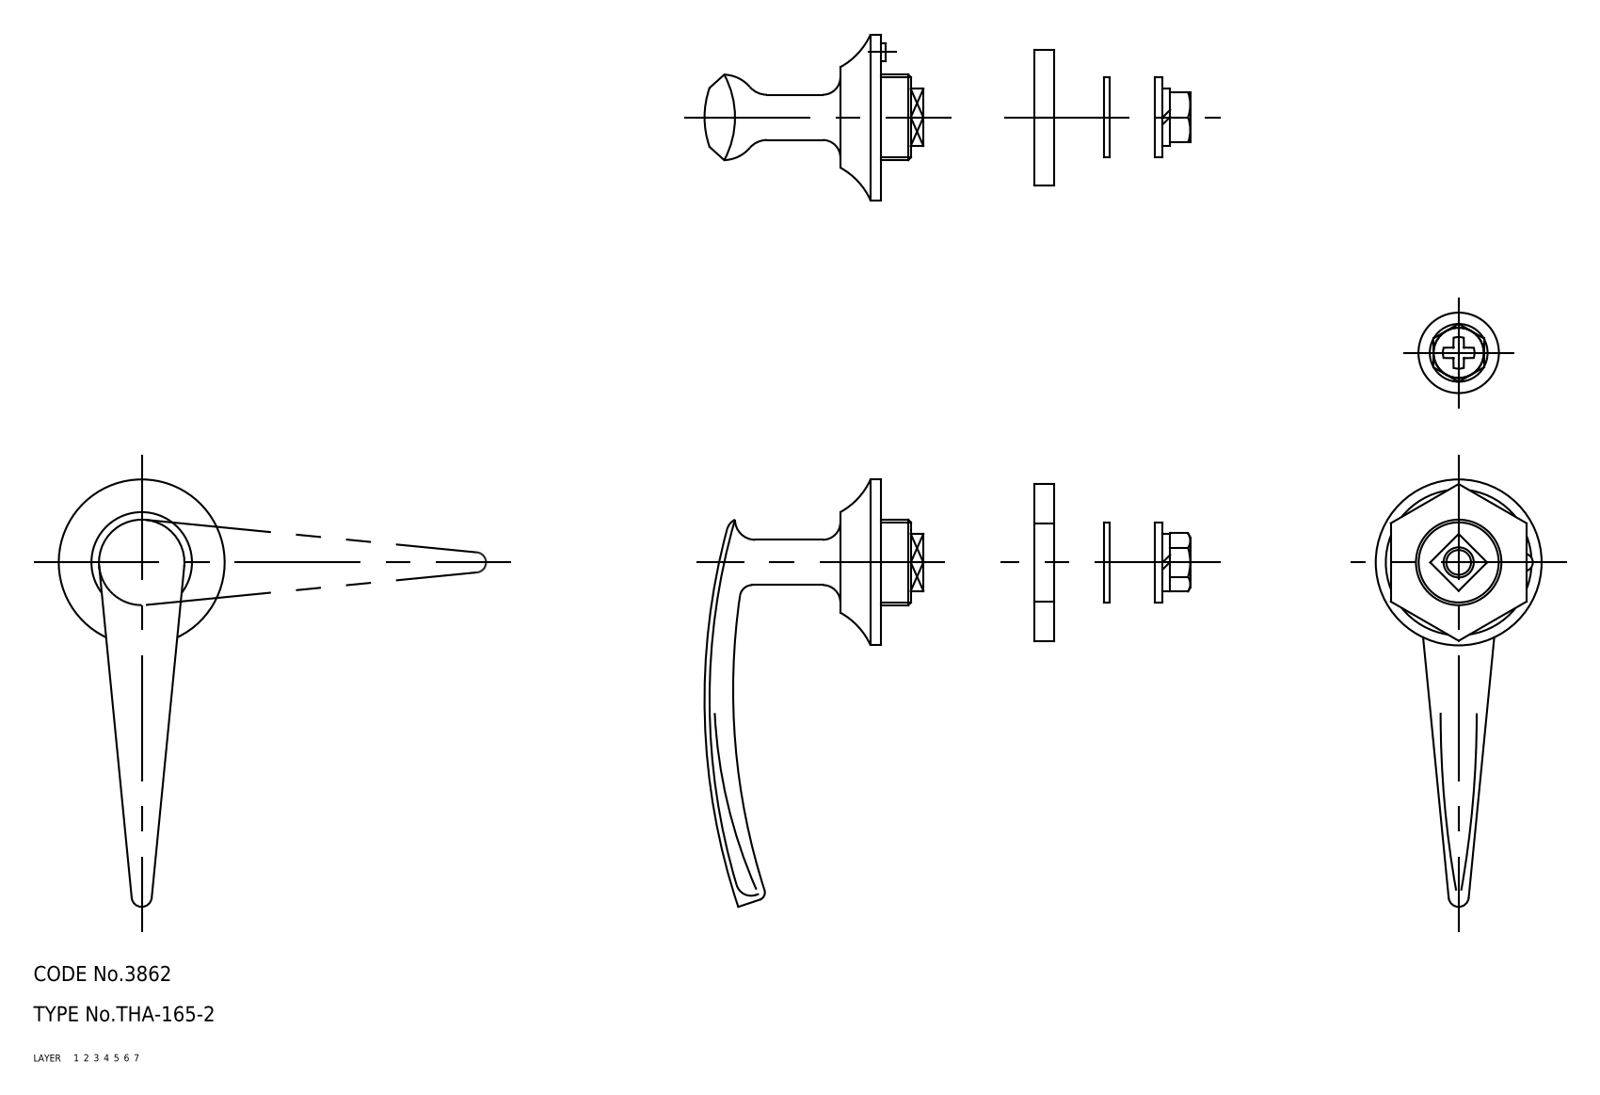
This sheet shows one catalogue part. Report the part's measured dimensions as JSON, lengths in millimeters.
{"part_name": "67117347; 67117360; 67117373; 67117386 (+3 more)", "step_written_by": "CADfix (AUTOMOTIVE_DESIGN)", "units": "millimeters", "bodies": {"solids": 7, "faces": 117, "planar": 0, "cylindrical": 0, "other": 117}, "overall_size": [85, 50.63, 33], "volume_mm3": 13057, "surface_area_mm2": 9397}
